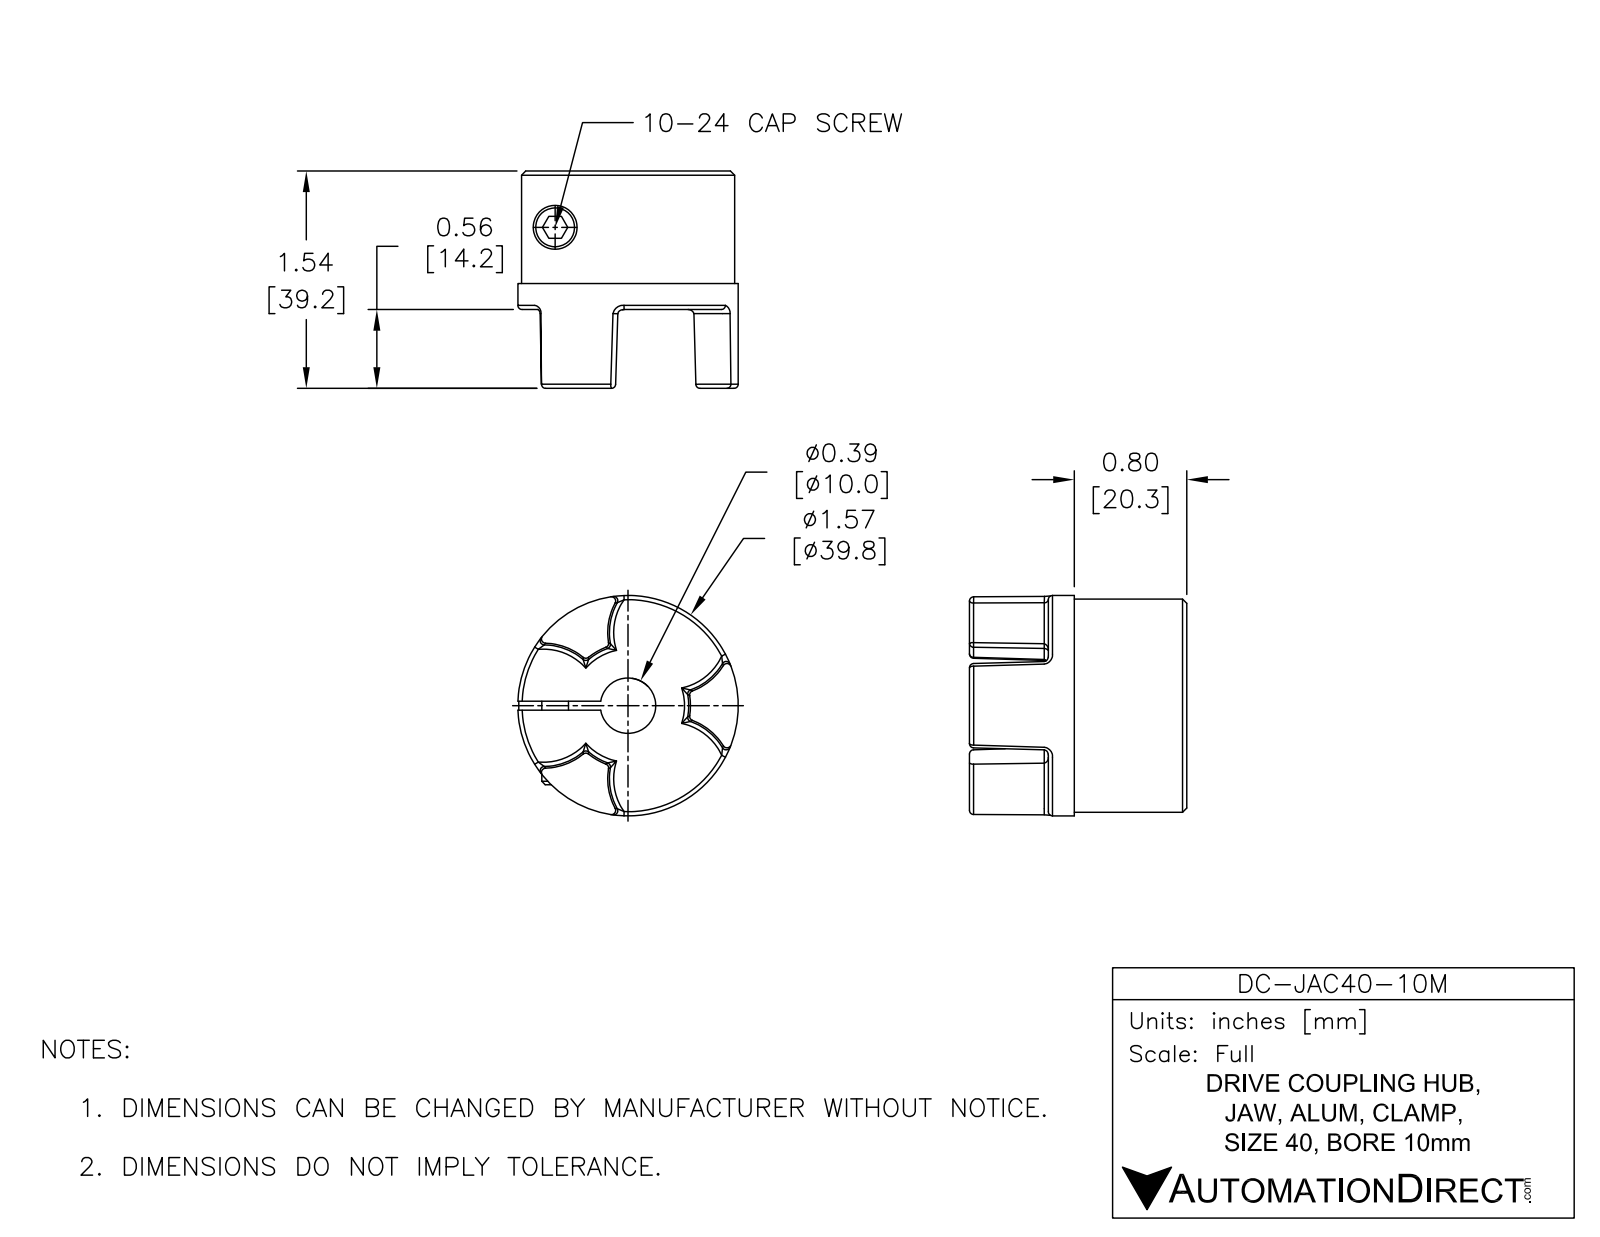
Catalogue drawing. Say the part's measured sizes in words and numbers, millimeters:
The part is named "DC-JAC40-10M". Its 3-D file was written by "SolidWorks 2015 (AUTOMOTIVE_DESIGN)". It is 1 solid with 100 faces: 12 planar, 16 cylindrical and 72 other. Overall it measures 39.78 by 39.76 by 39.22 millimeters. Its volume is 29 761 cubic millimeters and its surface area 8 675 square millimeters. Round holes: 1 of diameter 5.11, 1 of diameter 8.36, 1 of diameter 10. Round bosses or shafts: 1 of diameter 39.78, 1 of diameter 38.48. Partial cylindrical surfaces (rounded edges, fillets, slot ends): 1 of radius 12.48. The main face-to-face distances are 24.99, 1.6, 39.22, 14.23, 20.29, 4.7, 18.93, 3.99, 5.59.
